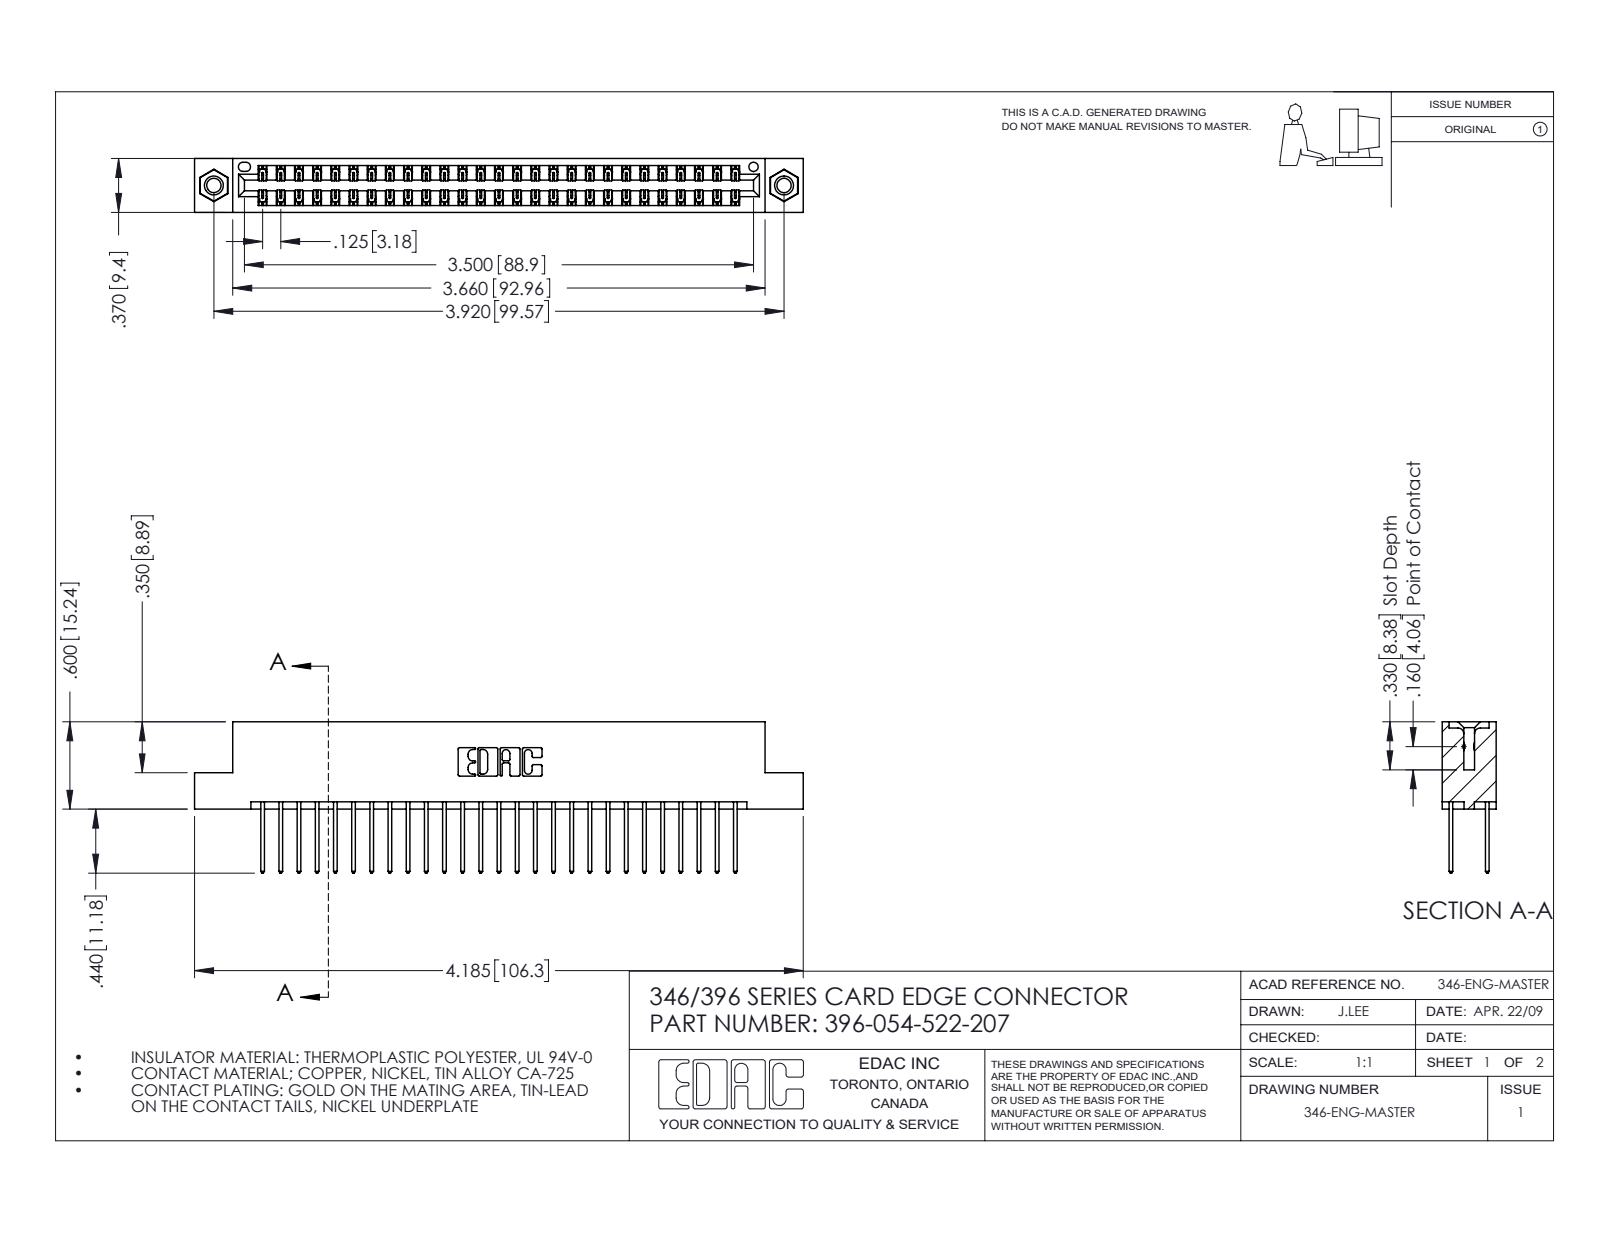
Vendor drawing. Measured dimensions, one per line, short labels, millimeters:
name: 345-250-001_345-250-005-103; 345-292-001_345-293-122; 346 Part_Flush Mounting Lugs - 0.156 Dia-TI; 396-054-522-207
written by: SolidWorks 2016 (CONFIG_CONTROL_DESIGN)
unit: mm
bodies: 57 solids, 2990 faces (1998 planar, 976 cylindrical, 16 other)
size: 106.3 × 26.4 × 9.4
volume: 10 400 mm³; area: 14 700 mm²
holes: 2× ⌀2.5, 2× ⌀3.2, 2× ⌀4, 1× ⌀1.6
bosses: 2× ⌀3.9
rounds: 81× R0.2, 54× R0.3, 22× R0.3, 6× R0.2, 6× R0.8, 3× R0.7, 2× R0.4, 2× R0.6
face distances: 1.2, 8.2, 6.4, 9.4, 1.8, 7.6, 0.6, 7, 3.8, 5.6
hole spacings: 6.2, 94.3, 99.6
